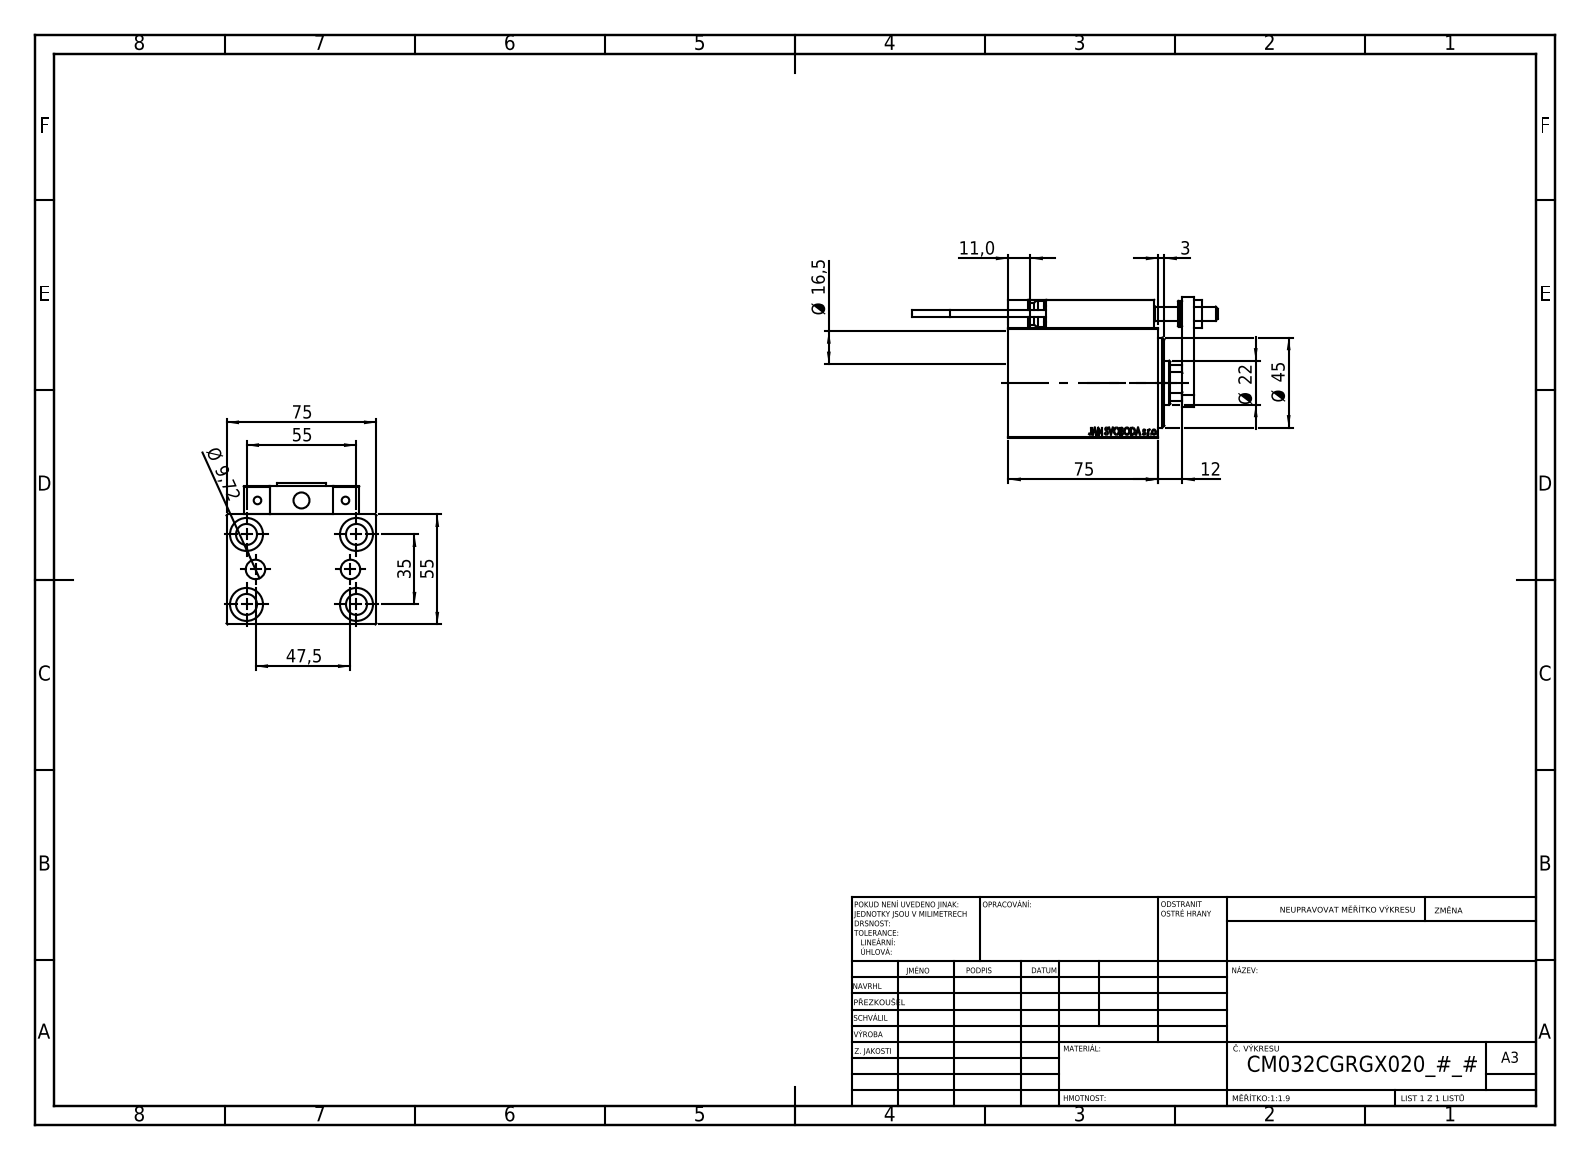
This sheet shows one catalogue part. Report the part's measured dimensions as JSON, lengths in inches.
{"part_name": "Block; ALLEN BOLT D5; SWITCH DIM B,W; V450CM_VC_B (+7 more)", "step_written_by": "SolidWorks 2019 (CONFIG_CONTROL_DESIGN)", "units": "inches", "bodies": {"solids": 23, "faces": 1272, "planar": 558, "cylindrical": 180, "other": 534}, "overall_size": [6.012, 2.953, 2.776], "volume_in3": 19.25, "surface_area_in2": 130, "round_holes": [[0.315, 5], [0.413, 5], [0.65, 5], [0.126, 4], [0.157, 4], [0.197, 2], [0.383, 2], [0.276, 1], [0.866, 1], [1.004, 1], [1.26, 1], [1.339, 1]], "round_bosses_or_shafts": [[0.197, 2], [0.15, 2], [0.512, 1], [0.433, 1]], "partial_cylinders_radius": [[0.012, 30], [0.118, 2], [0.413, 1]], "face_to_face_distances": [2.165, 2.953, 0.394, 0.551, 0.472, 0.276, 2.717, 0.984, 0.787, 0.591], "hole_center_spacings": [1.283, 0.448, 0.699, 0.711, 0.787, 1.066, 1.165, 1.169]}
